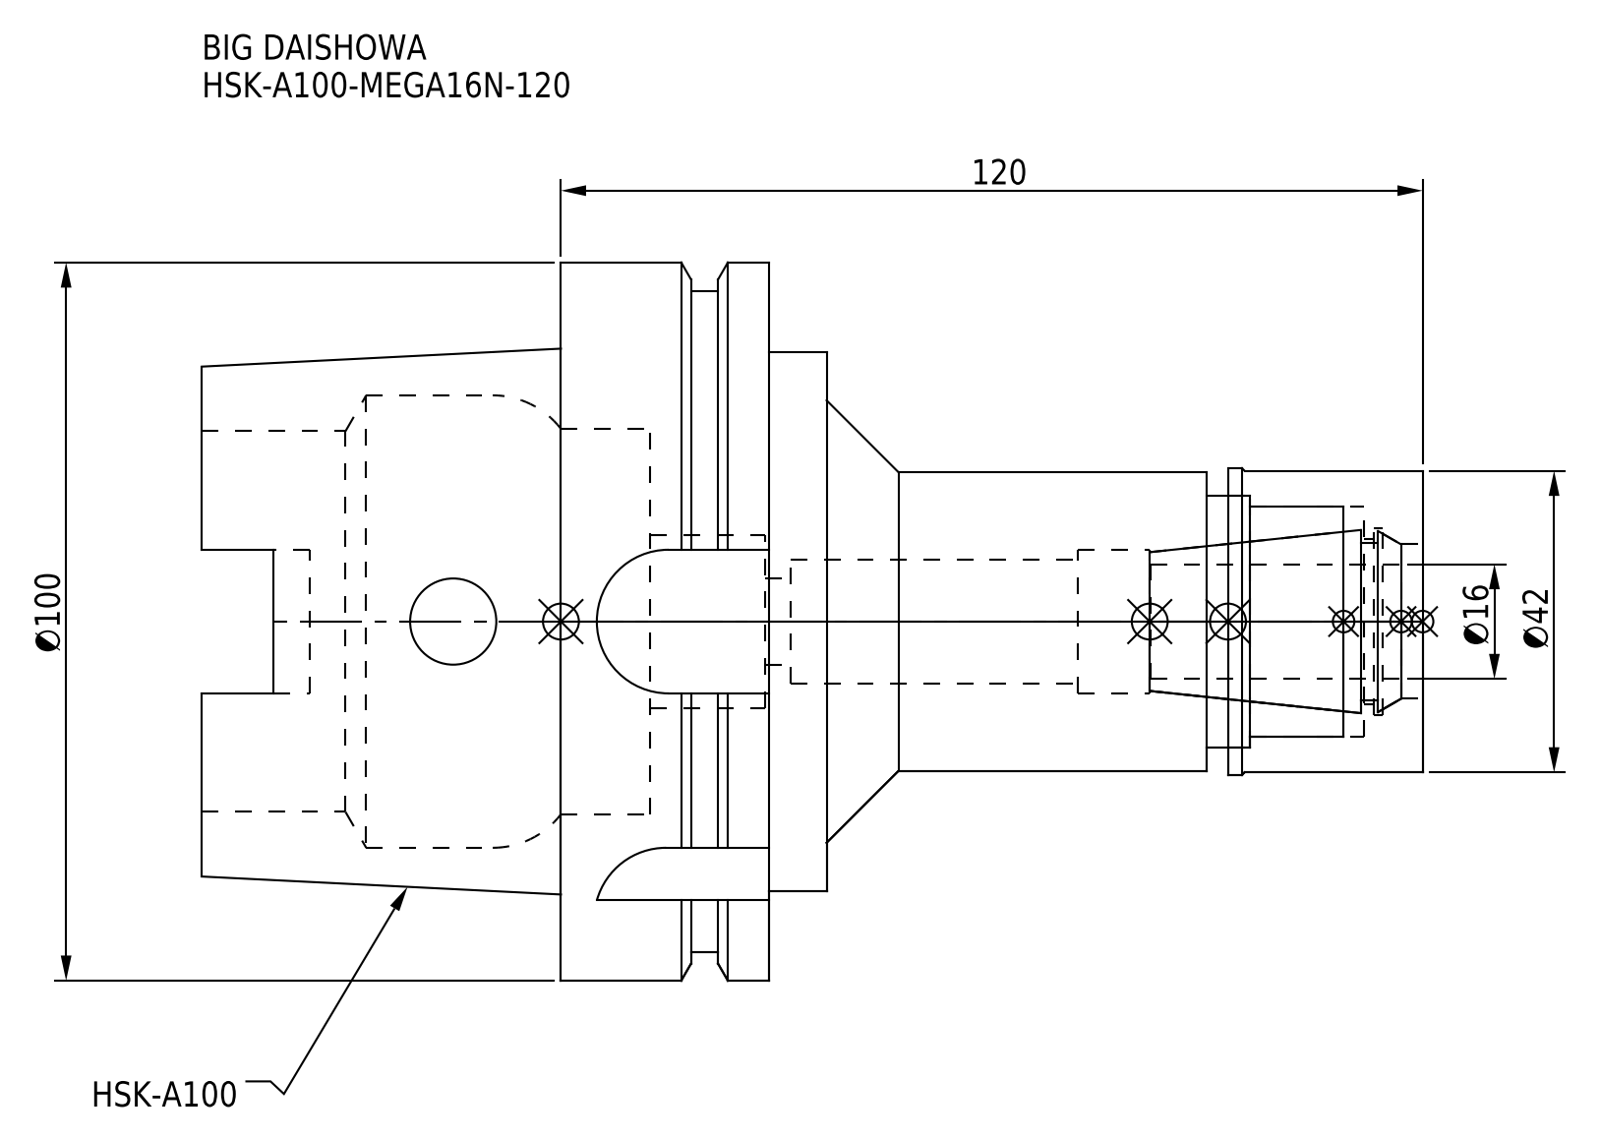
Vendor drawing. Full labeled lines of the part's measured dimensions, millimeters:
Part name (STEP PRODUCT): MGN16_1.stp; DXF_TEMP_ASSY_ASM_4_ASM.stp; HSK-A100-MEGA16N-120-160.stp; HSK-A100-MEGA16N-120_1.stp (+3 more)
STEP written by: SolidWorks 2019 (CONFIG_CONTROL_DESIGN)
Units: millimetres
Bodies: 2 solids, 124 faces (44 planar, 58 cylindrical, 22 other)
Overall size (bounding box): 170 × 100 × 100
Volume: 379 948 mm³ · Surface area: 72 948 mm²
Round holes (diameter × count): ⌀12 ×2, ⌀17.3 ×1, ⌀20 ×1, ⌀21.5 ×1, ⌀23 ×1, ⌀24 ×1, ⌀26 ×1, ⌀32 ×1, ⌀35 ×1, ⌀53 ×1, ⌀53.8 ×1, ⌀63 ×1
Round bosses / shafts (diameter × count): ⌀100 ×1, ⌀92 ×1, ⌀75 ×1, ⌀42.7 ×1, ⌀42 ×1, ⌀41.6 ×1
Partial cylindrical surfaces — rounded edges, fillets, slot ends (radius × count): R4.88 ×4, R10 ×4
Main face-to-face distances: 29, 16.55, 12.45, 37, 8, 24.55, 87, 79, 62.45, 50
